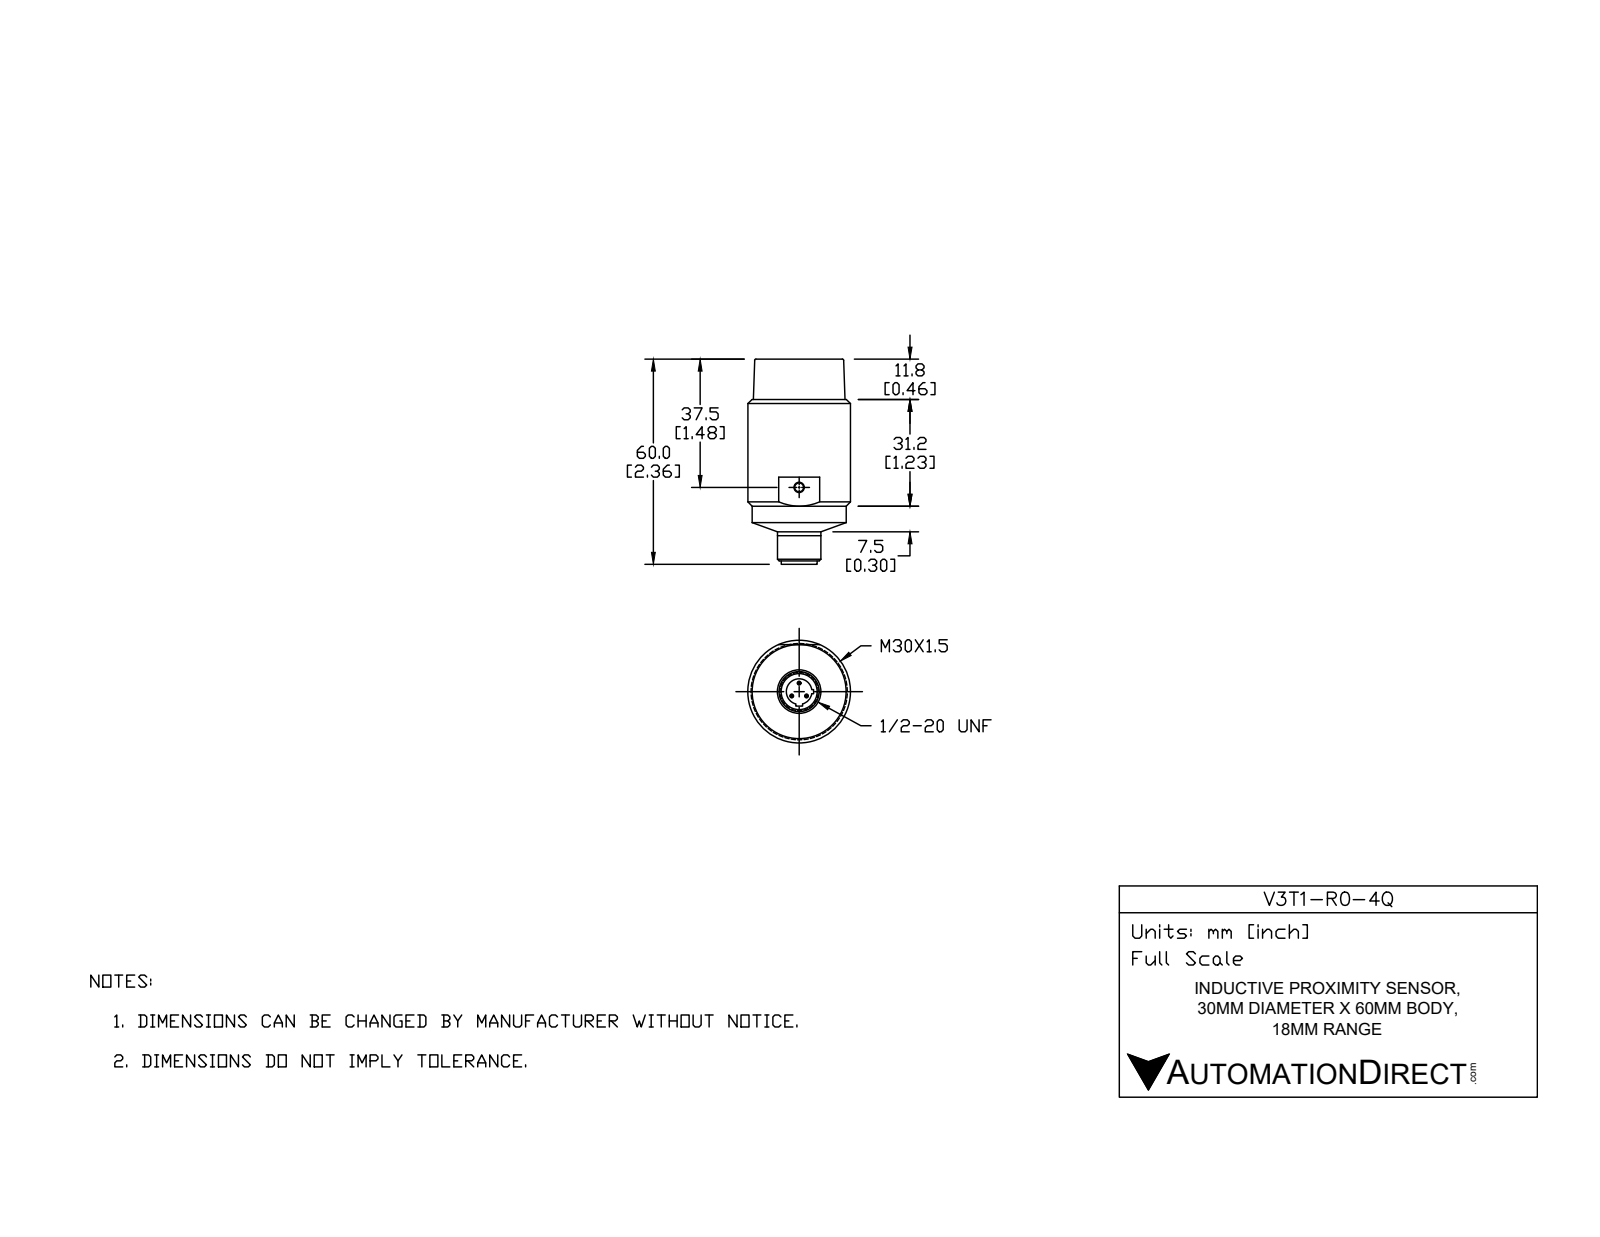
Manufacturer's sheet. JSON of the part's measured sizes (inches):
{"part_name": "V3T1_4Q_fig", "step_written_by": "ST-DEVELOPER v16.7 (AUTOMOTIVE_DESIGN)", "units": "inches", "bodies": {"solids": 4, "faces": 57, "planar": 24, "cylindrical": 19, "other": 14}, "overall_size": [2.362, 1.181, 1.181], "volume_in3": 1.058, "surface_area_in2": 15.76, "round_holes": [[0.039, 3], [0.102, 1], [0.295, 1], [0.374, 1], [0.906, 1], [1.024, 1]], "round_bosses_or_shafts": [[0.039, 3], [1.181, 1], [1.083, 1], [0.5, 1], [0.413, 1], [0.376, 1], [0.37, 1]], "face_to_face_distances": [0.472, 1.016, 0.543, 2.071, 1.598, 1.055, 2.083, 1.61, 1.067, 2.362], "hole_center_spacings": [0.098, 0.17, 0.171]}
